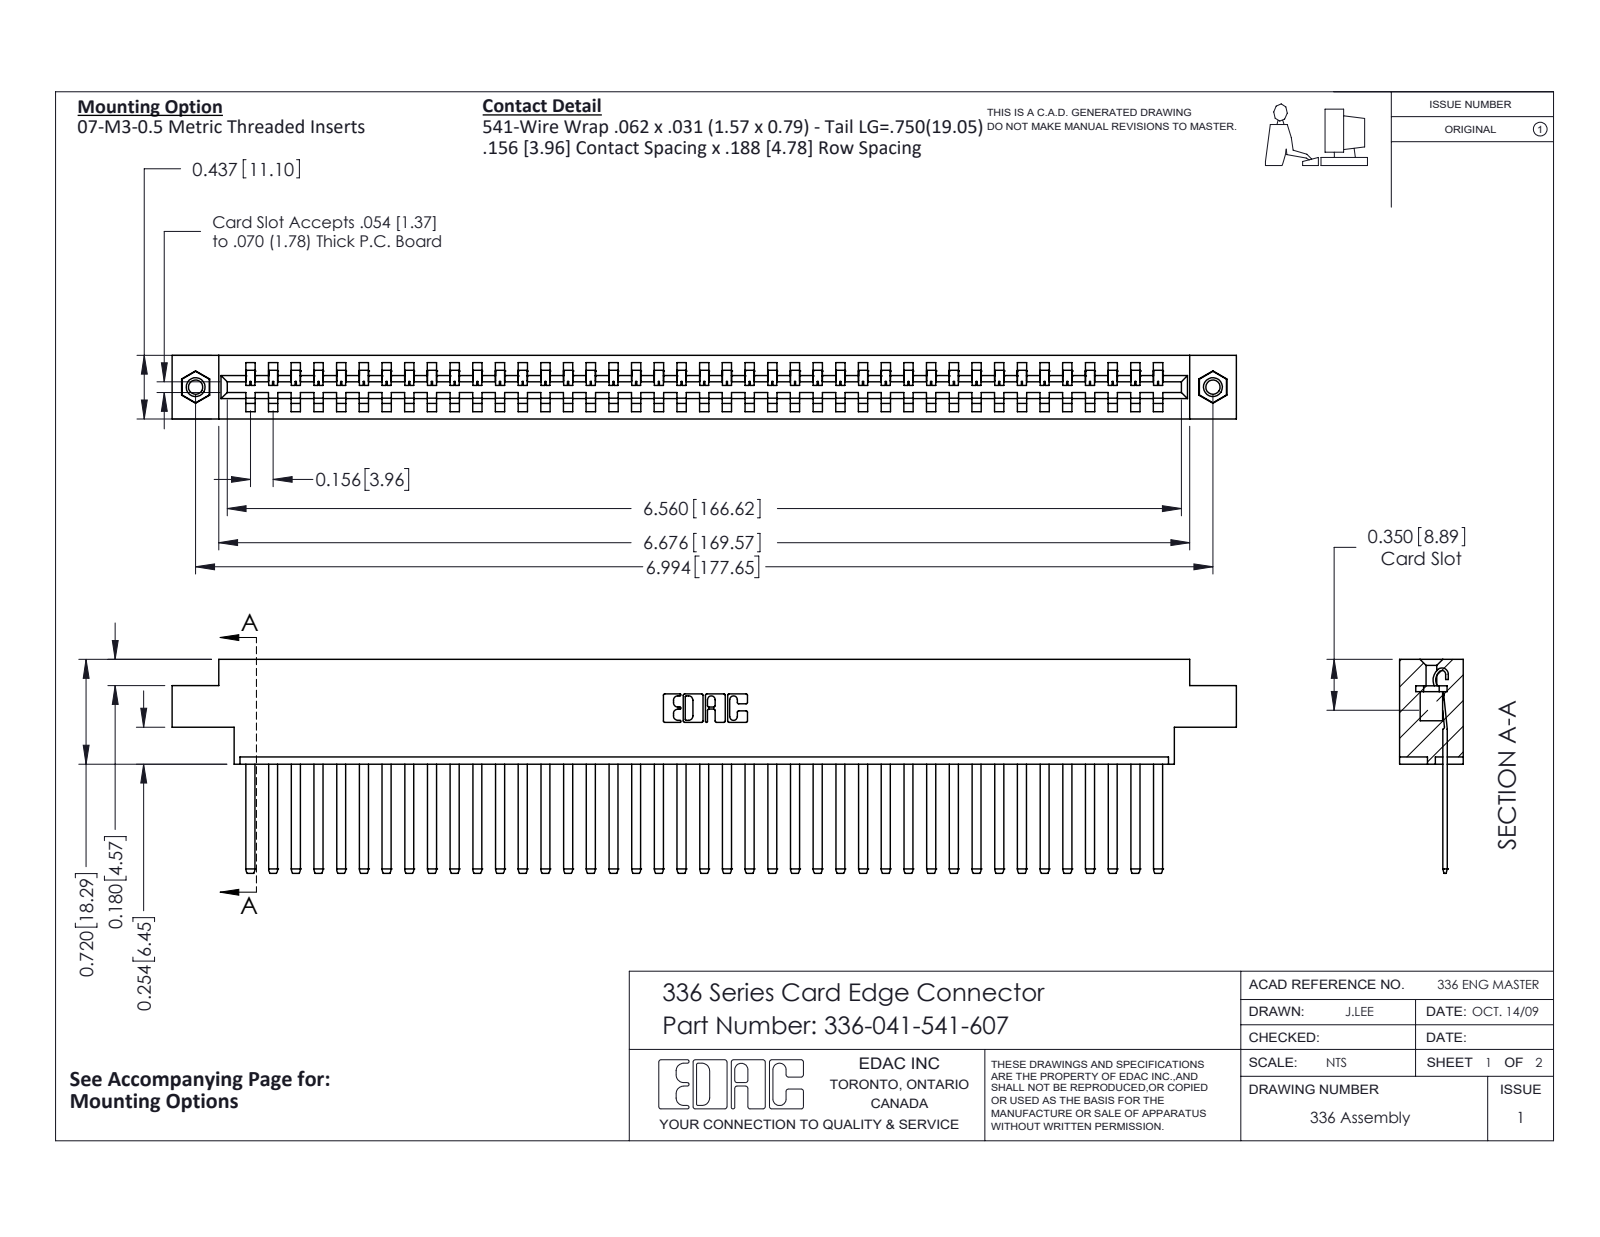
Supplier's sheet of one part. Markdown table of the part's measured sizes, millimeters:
| quantity | value |
| --- | --- |
| part name | 345-250-001_345-250-005-103; 336-041-541-607; 336-290-001_336-290-541; 336 Part_Offset - .156 Dia - TI |
| STEP written by | SolidWorks 2020 (CONFIG_CONTROL_DESIGN) |
| units | millimeters |
| bodies | 44 solids, 2228 faces (1500 planar, 712 cylindrical, 16 other) |
| overall size | 185.9 × 37.3 × 11.1 |
| volume | 27 040 mm³ |
| surface area | 29 540 mm² |
| round holes (diameter × count) | 2.5 × 2, 3.2 × 2, 4 × 2 |
| round bosses / shafts (diameter × count) | 3.9 × 2 |
| partial cylindrical surfaces (radius × count) | 0.1 × 82, 1.4 × 82, 0.3 × 22, 0.2 × 6, 0.8 × 6, 0.7 × 3, 0.6 × 2, 1 × 2 |
| main face-to-face distances | 11.1, 4.6, 8.3, 3.6, 7.5, 2.8, 0.8, 6.5, 1.3, 3.3 |
| hole center spacings | 177.6 |
